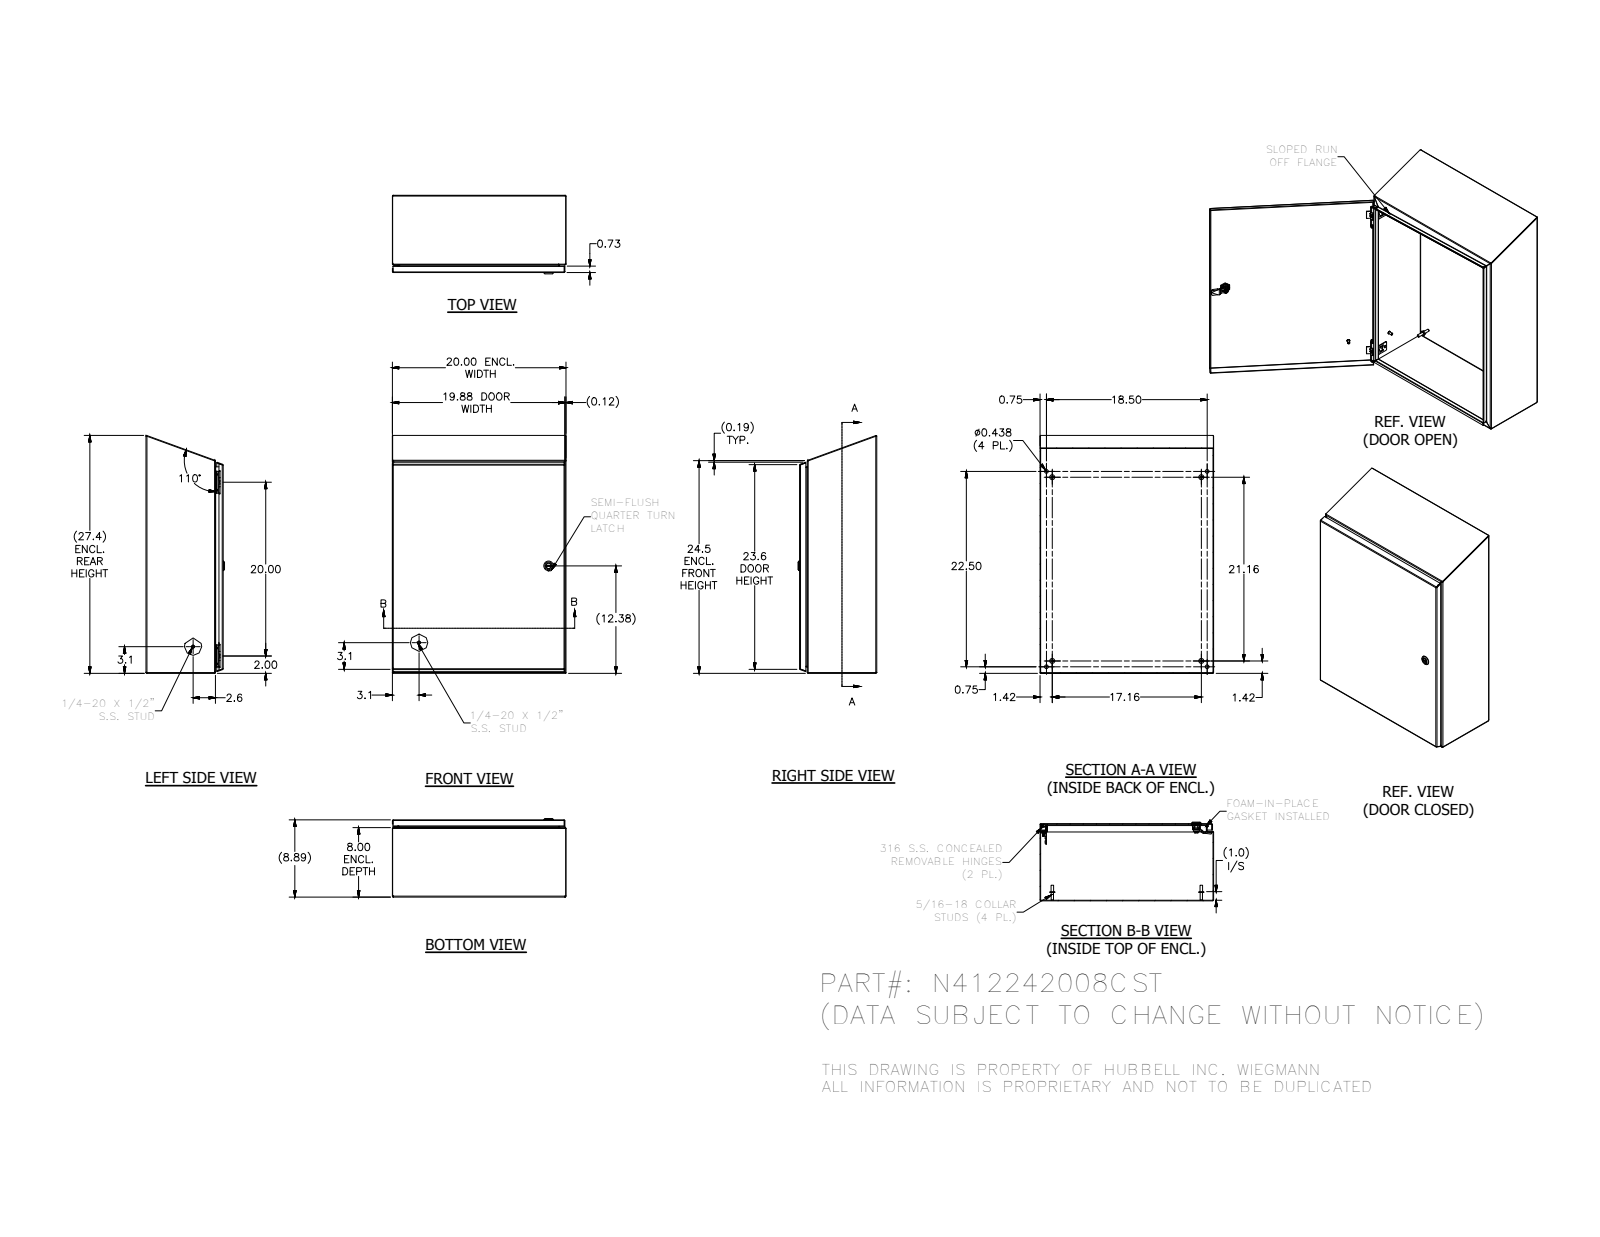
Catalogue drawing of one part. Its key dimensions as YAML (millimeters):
part_name: "N412242008CST"
step_written_by: "SolidWorks 2018 (AUTOMOTIVE_DESIGN)"
units: millimeters
bodies: {solids: 36, faces: 1521, planar: 568, cylindrical: 552, other: 401}
overall_size: [695.7, 508, 229.7]
volume: 2376000
surface_area: 2542000
round_holes:
  - {diameter: 2.4, count: 4}
  - {diameter: 3.9, count: 4}
  - {diameter: 4.2, count: 4}
  - {diameter: 4.4, count: 4}
  - {diameter: 4.7, count: 4}
  - {diameter: 11.1, count: 4}
  - {diameter: 4, count: 3}
  - {diameter: 4.7, count: 1}
  - {diameter: 5, count: 1}
  - {diameter: 8, count: 1}
  - {diameter: 10, count: 1}
  - {diameter: 10.2, count: 1}
round_bosses_or_shafts:
  - {diameter: 6.4, count: 10}
  - {diameter: 14.3, count: 4}
  - {diameter: 9.1, count: 4}
  - {diameter: 8.1, count: 4}
  - {diameter: 7.6, count: 4}
  - {diameter: 7, count: 4}
  - {diameter: 6.5, count: 4}
  - {diameter: 4.2, count: 4}
partial_cylinders:
  - {radius: 0.3, count: 30}
  - {radius: 0.8, count: 29}
  - {radius: 1.3, count: 26}
  - {radius: 2.7, count: 19}
  - {radius: 0.4, count: 18}
  - {radius: 3.2, count: 16}
  - {radius: 0.5, count: 13}
  - {radius: 0.8, count: 8}
face_to_face_distances: [1.9, 223.9, 222, 225.7, 506.1, 508, 504.2, 201.3, 22.5, 20.7]
hole_center_spacings: [508, 479.3, 12.7, 16.7, 16.8, 25, 33.2, 33.3]
